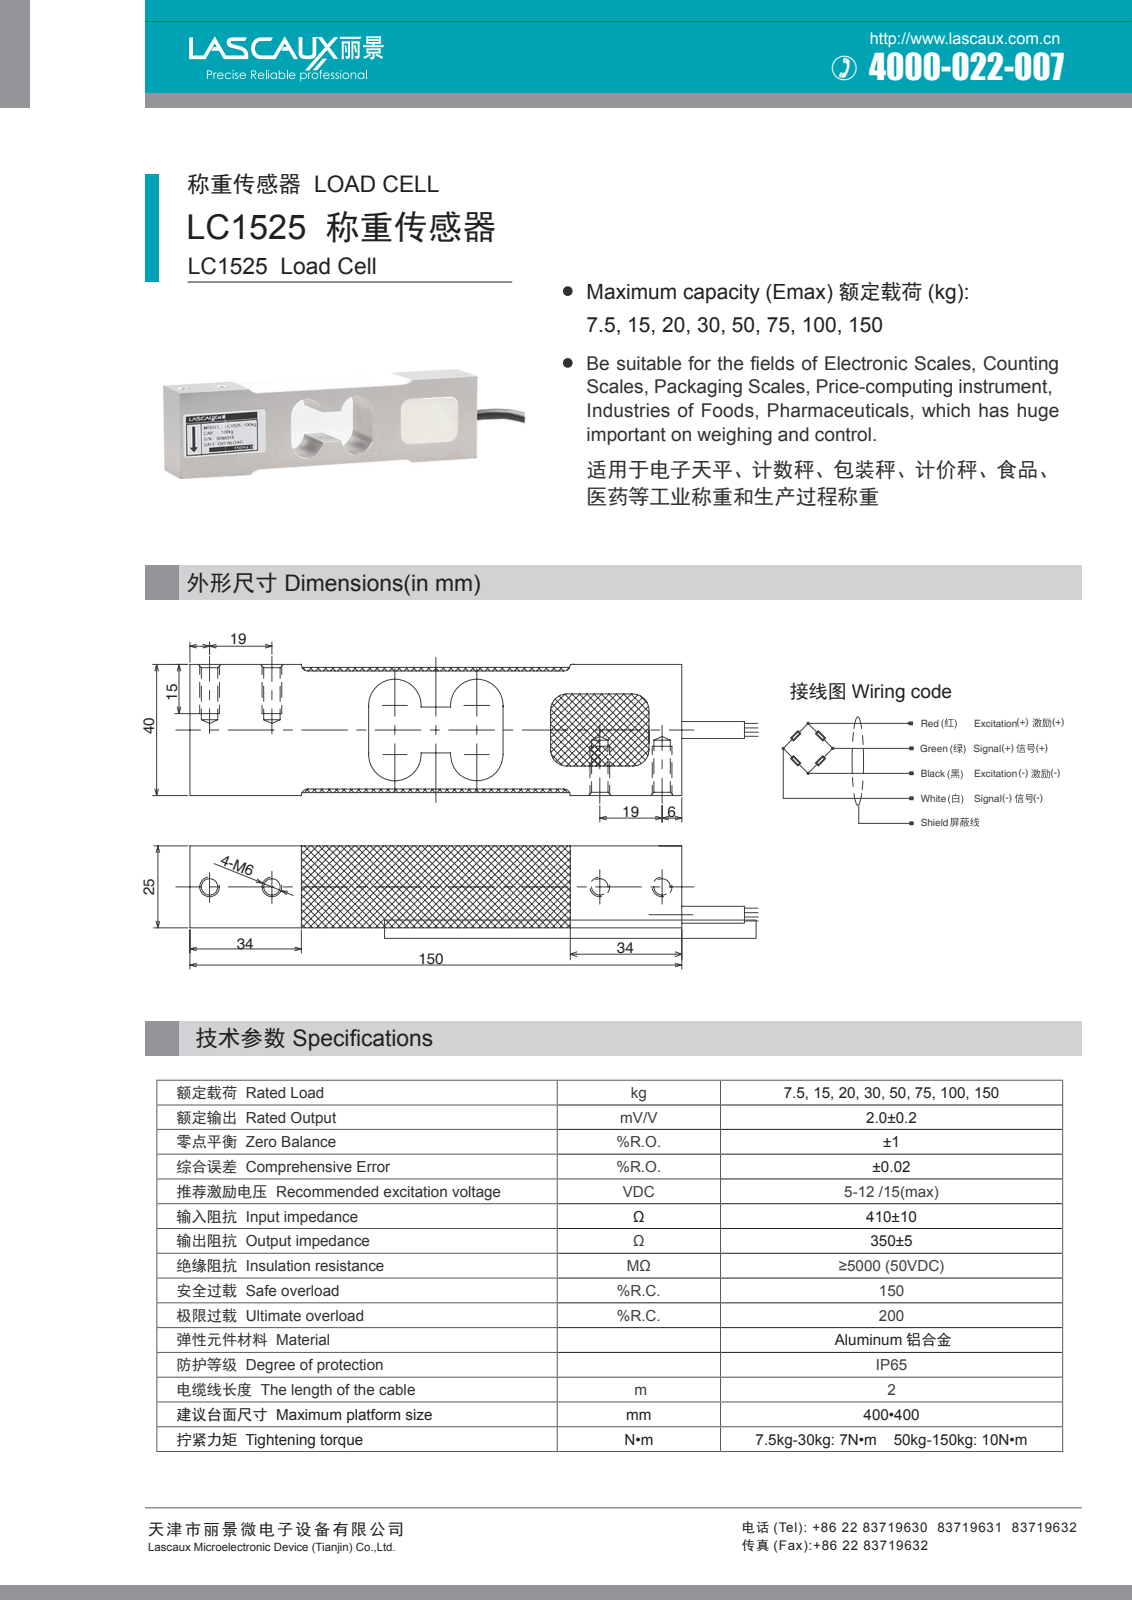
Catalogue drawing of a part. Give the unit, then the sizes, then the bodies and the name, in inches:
Units: inches
Overall size (bounding box): 5.906 × 1.772 × 0.984
Round holes (diameter × count): ⌀0.197 ×4
Partial cylindrical surfaces — rounded edges, fillets, slot ends (radius × count): R0.039 ×4, R0.295 ×4
Main face-to-face distances: 0.984, 0.079, 1.693, 1.614, 1.772, 5.906, 2.264, 3.642, 1.378, 0.531
Hole centre spacings: 0.748, 4.685, 3.937, 5.433
Volume: 8.224 in³ · Surface area: 39.13 in²
Bodies: 1 solid, 42 faces (18 planar, 16 cylindrical, 8 other)
Part name (STEP PRODUCT): LC1525
STEP written by: SolidWorks 2016 (CONFIG_CONTROL_DESIGN)
